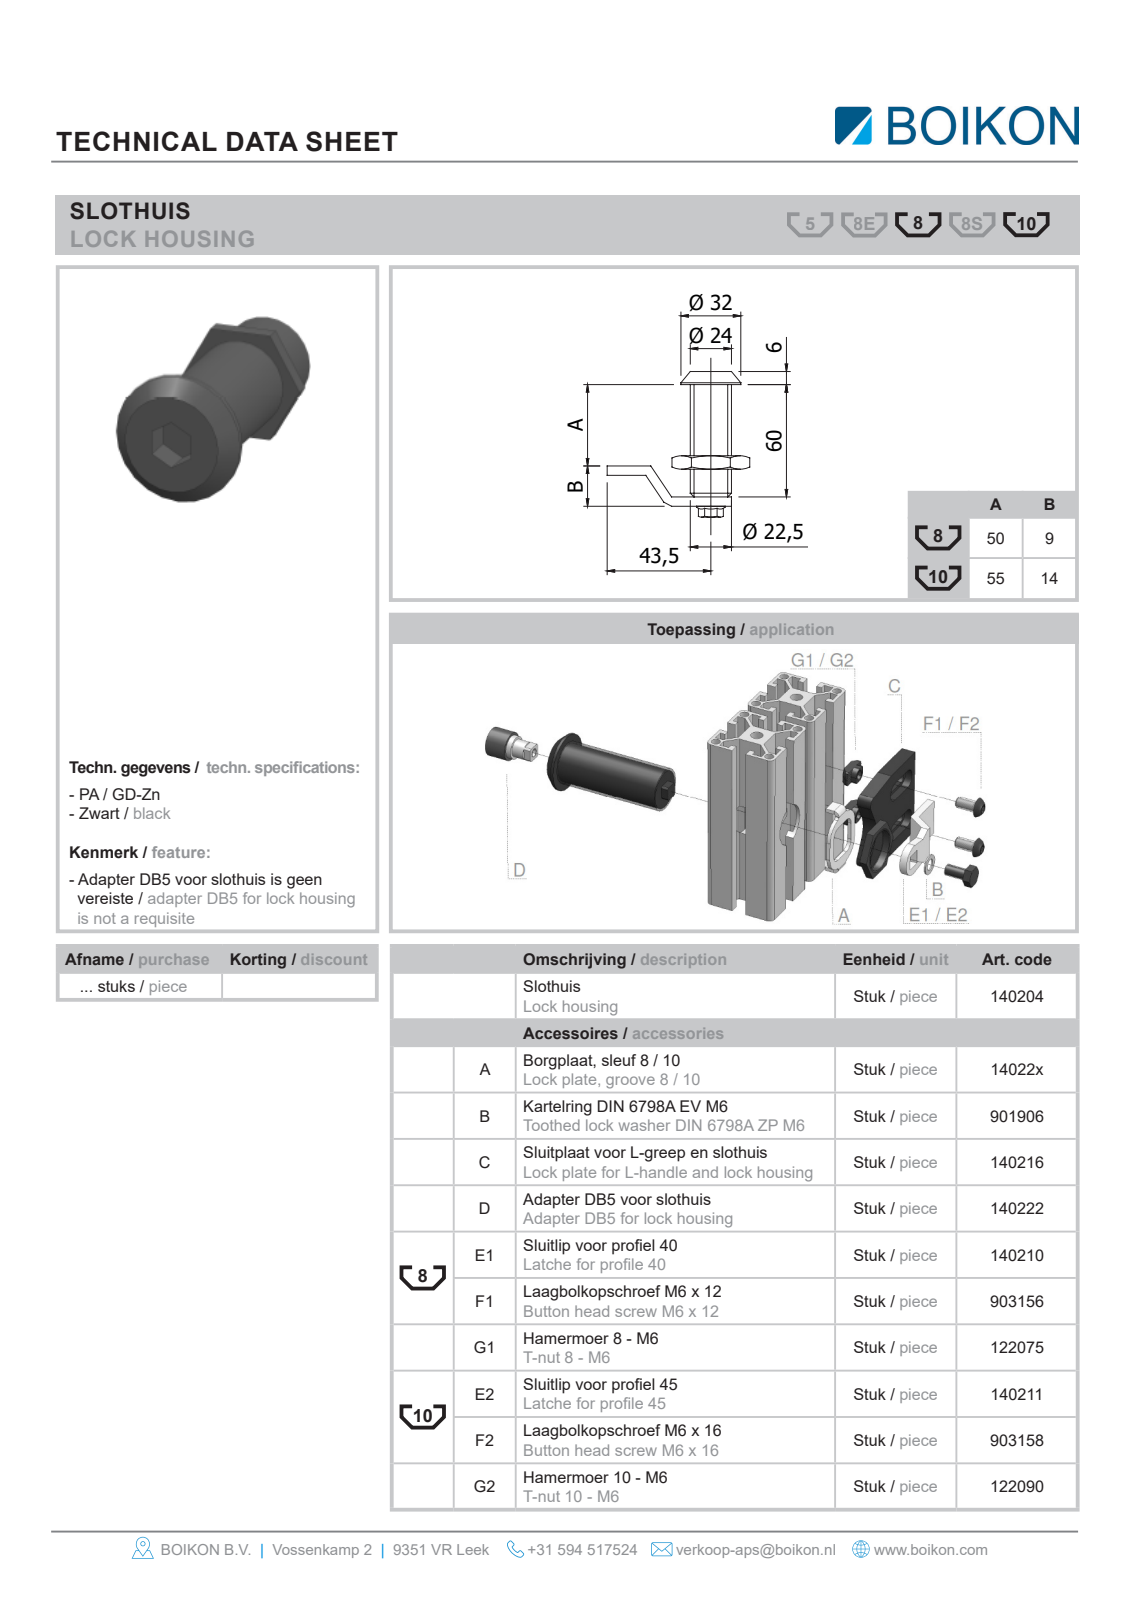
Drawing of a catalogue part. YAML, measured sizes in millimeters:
part_name: "Root; 140204Slothuis compleetBOIKON; 901906Kartelring DIN 6798A EV M6BOIKON0; 140211Sluitlip 45 profielBOIKON (+4 more)"
step_written_by: "HiCAD 2013 1802.4 Build 509 (AUTOMOTIVE_DESIGN)"
units: millimeters
bodies: {solids: 9, faces: 114, planar: 86, cylindrical: 27, other: 1}
overall_size: [75, 59.5, 38.2]
volume: 33703
surface_area: 12482
round_holes:
  - {diameter: 6.4, count: 1}
  - {diameter: 22, count: 1}
round_bosses_or_shafts:
  - {diameter: 32, count: 1}
  - {diameter: 22.5, count: 1}
  - {diameter: 11, count: 1}
  - {diameter: 6, count: 1}
partial_cylinders:
  - {radius: 5, count: 5}
  - {radius: 2, count: 4}
  - {radius: 10, count: 4}
  - {radius: 1, count: 2}
  - {radius: 3, count: 2}
  - {radius: 8.5, count: 1}
face_to_face_distances: [4, 6, 5, 13, 8, 9, 2, 15, 1, 10]
